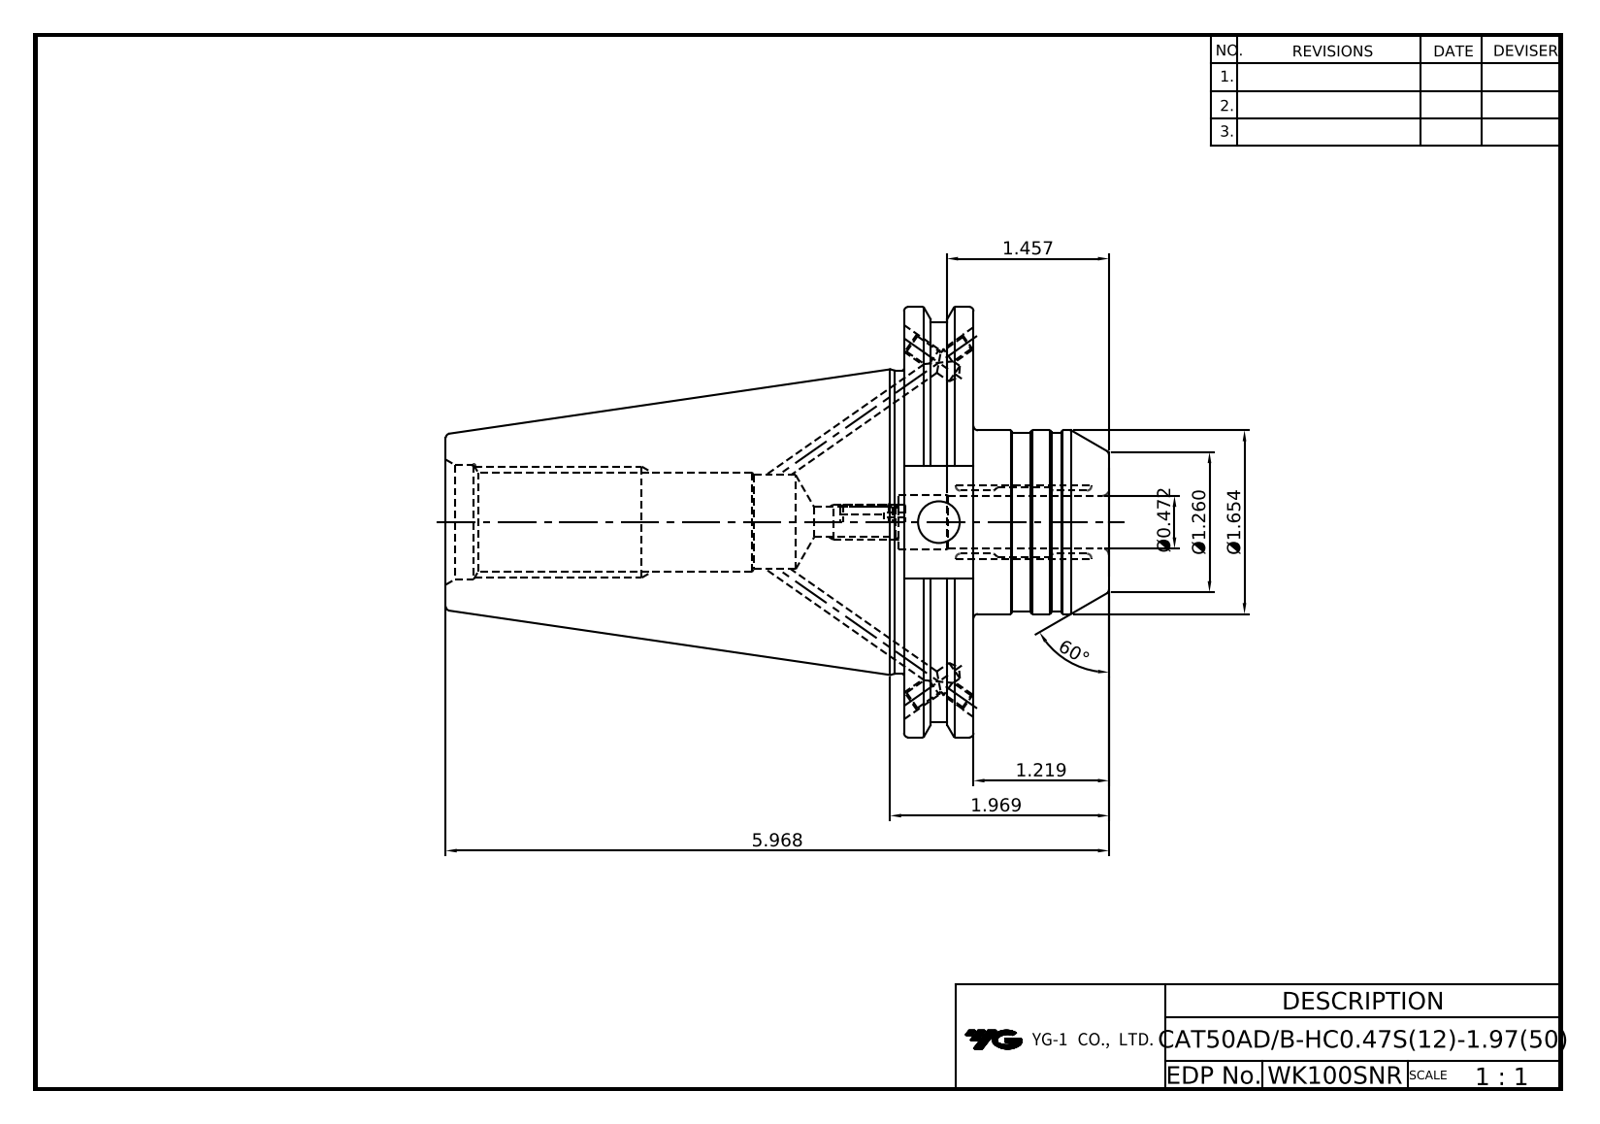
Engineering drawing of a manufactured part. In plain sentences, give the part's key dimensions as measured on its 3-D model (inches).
The part is named "LO-CAT50ADB-HC12S-50". Its 3-D file was written by "Autodesk Inventor 2025 (AUTOMOTIVE_DESIGN)". It is 1 solid with 98 faces: 33 planar, 31 cylindrical and 34 other. Overall it measures 5.969 by 3.875 by 3.728 inches. Its volume is 22.32 cubic inches and its surface area 76 square inches. Round holes: 4 of diameter 0.163, 4 of diameter 0.197, 1 of diameter 0.272, 1 of diameter 0.375, 1 of diameter 0.472, 1 of diameter 0.496, 1 of diameter 0.807, 1 of diameter 0.865, 1 of diameter 1.031. Round bosses or shafts: 1 of diameter 3.875, 1 of diameter 3.594, 1 of diameter 2.726, 1 of diameter 1.654, 1 of diameter 1.614. The main face-to-face distances are 0.625, 1.844, 1.219, 4.125, 4.75, 5.969, 2.875, 1.02, 0.151, 0.238. The hole center spacings are 2.35.
